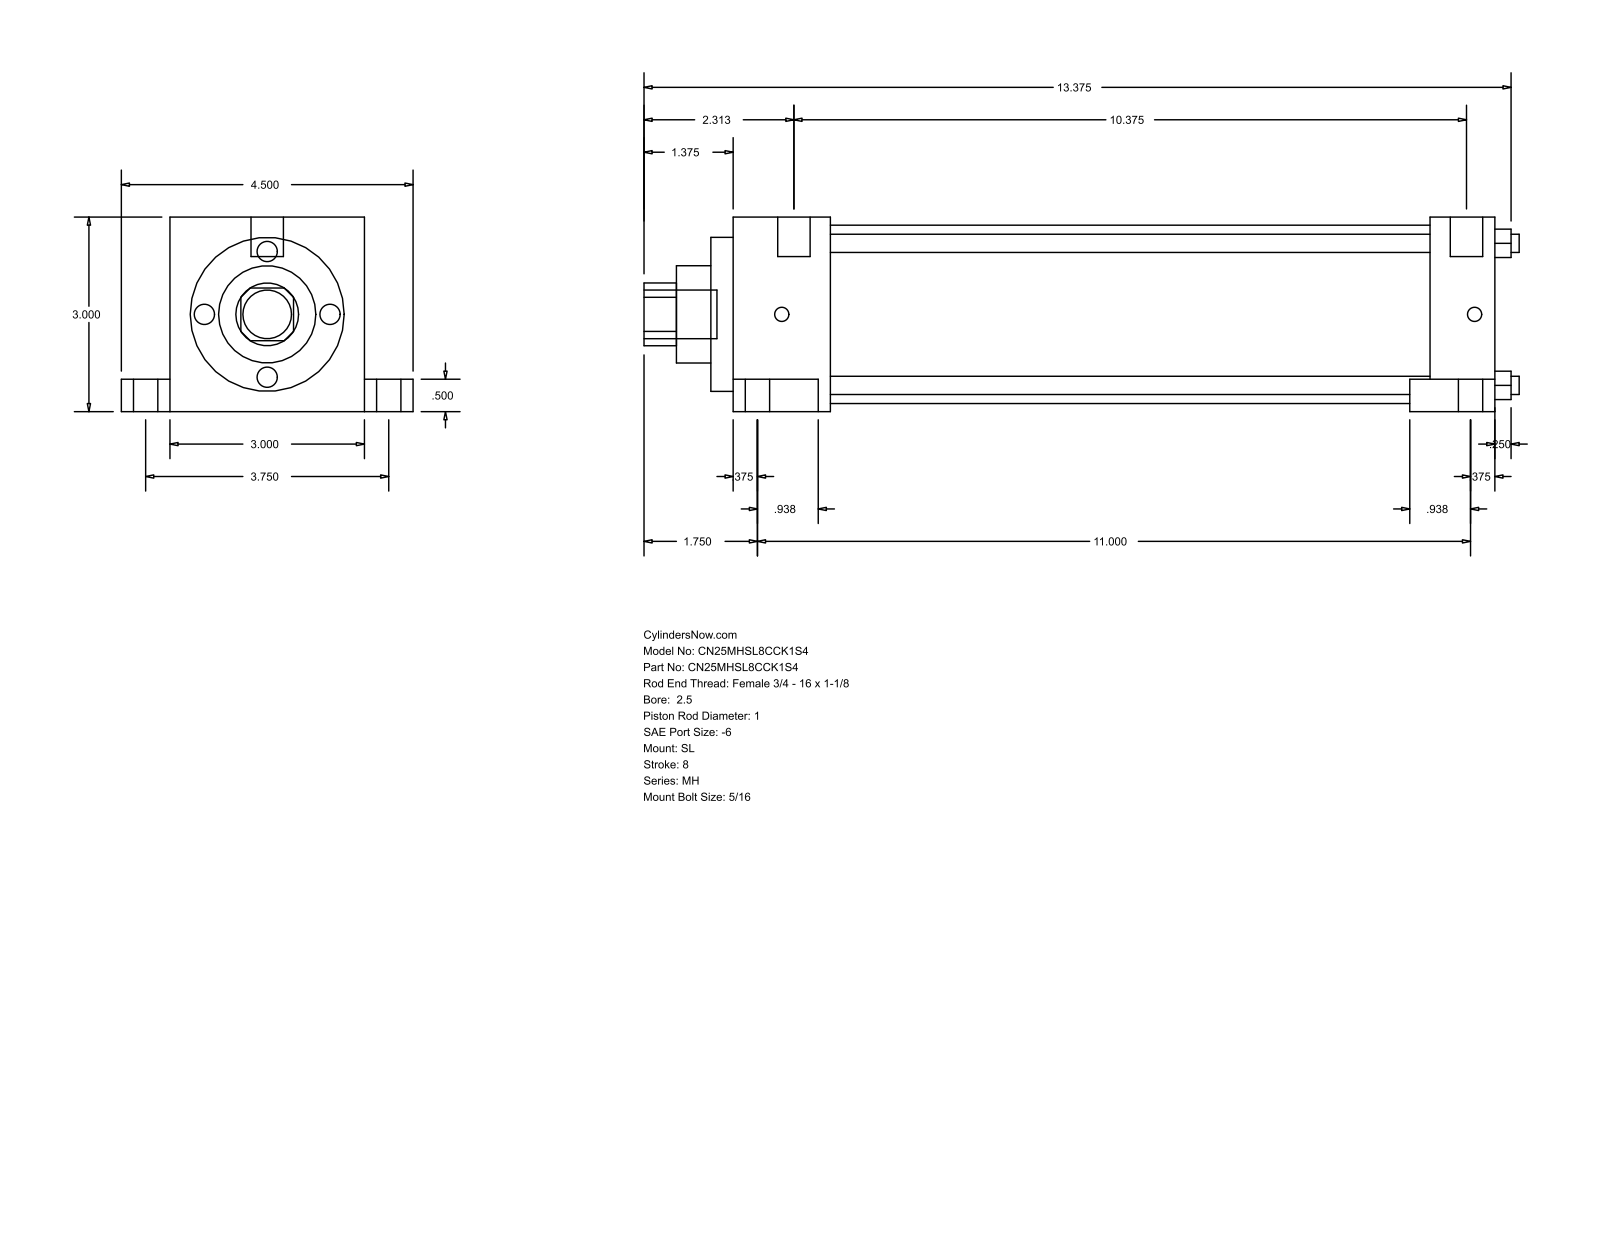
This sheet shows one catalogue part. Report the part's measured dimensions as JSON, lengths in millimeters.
{"part_name": "MH_SL__0250_1", "step_written_by": "GSSL Pune (CONFIG_CONTROL_DESIGN)", "units": "millimeters", "bodies": {"solids": 0, "faces": 86, "planar": 61, "cylindrical": 25, "other": 0}, "overall_size": [342.9, 114.3, 76.2], "round_holes": [[7.14, 4], [25.4, 1], [38.1, 1], [60.33, 1], [69.85, 1]], "round_bosses_or_shafts": [[15.88, 2], [9.53, 2], [5.56, 2], [19.05, 1], [12.7, 1]], "partial_cylinders_radius": [[12.29, 1]], "face_to_face_distances": [76.2, 25.4, 281.79, 307.19, 12.7, 63.5, 19.05, 95.25, 13.49, 295.28], "hole_center_spacings": [39.33, 55.62, 78.66]}
